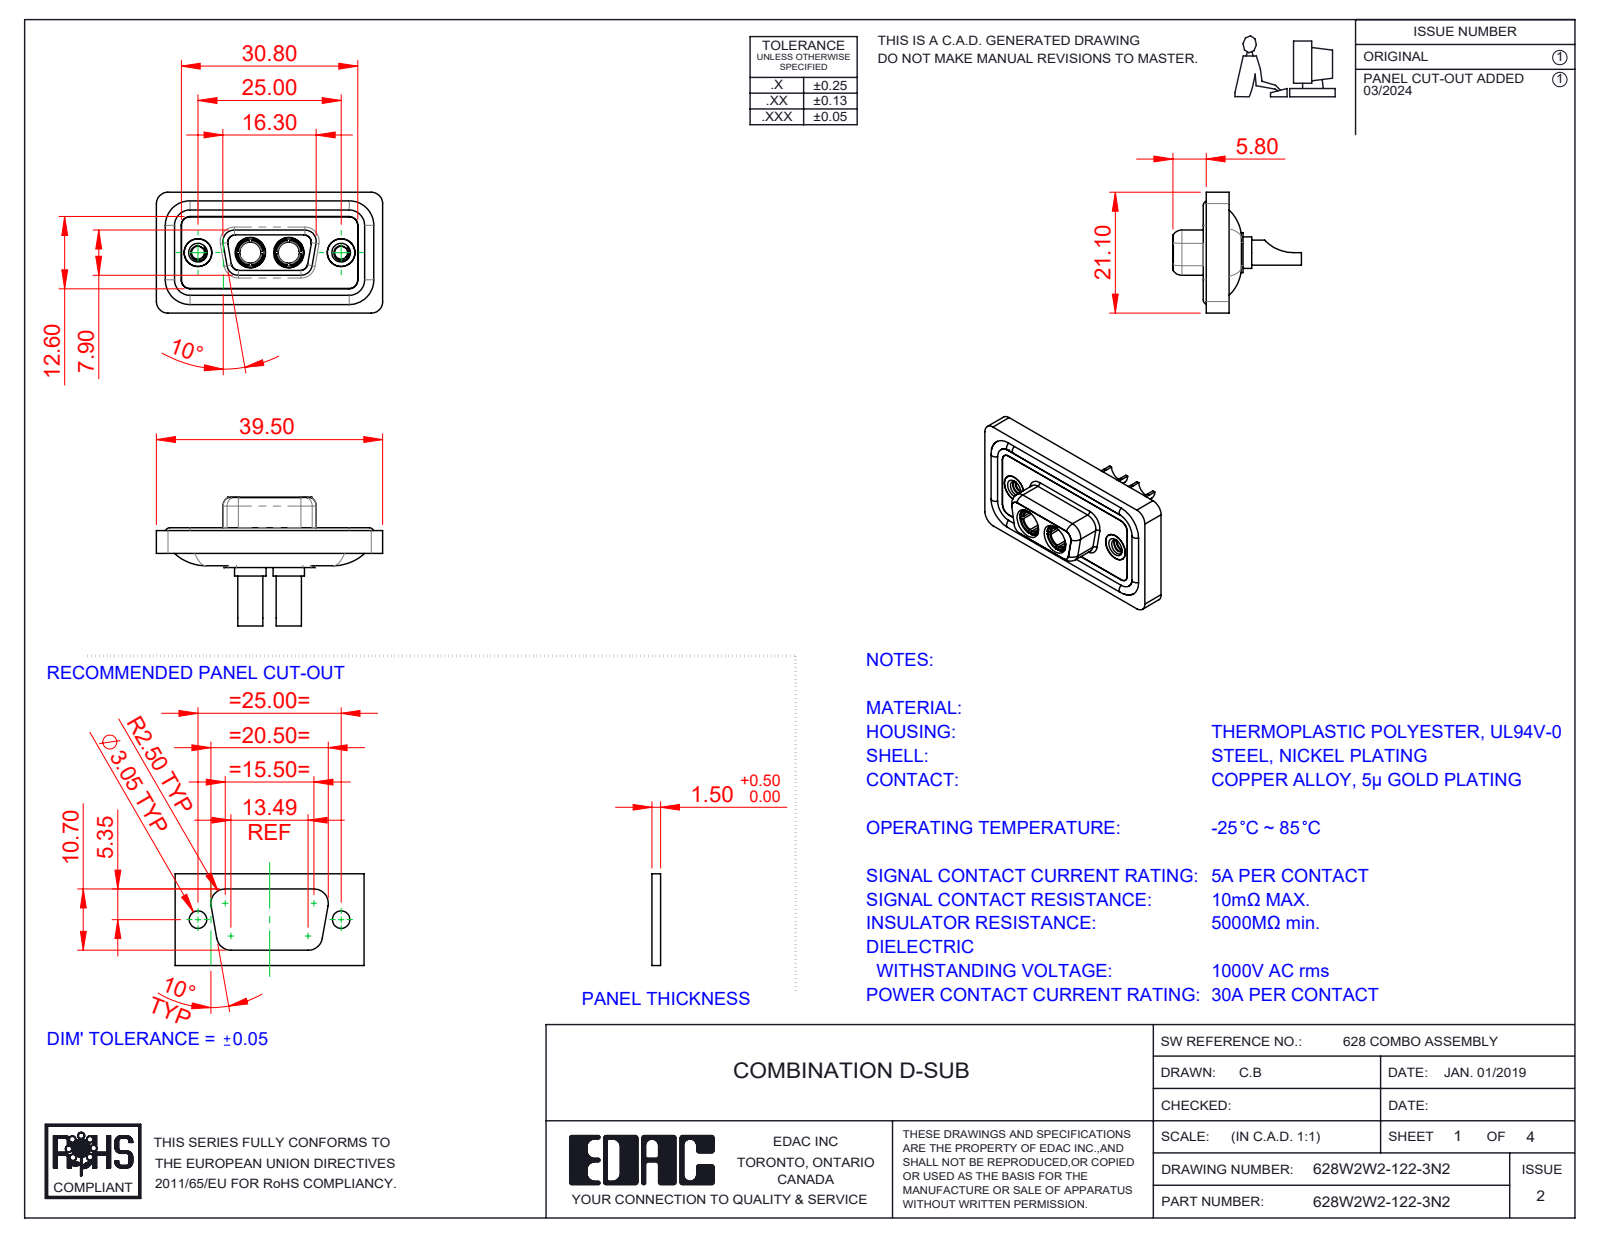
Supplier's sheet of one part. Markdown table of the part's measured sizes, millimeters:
| quantity | value |
| --- | --- |
| part name | 628Combo Shell Rear_09 Contacts; 628Combo Shell Front_09 Contacts; 628Combo Waterproof Housing_09 Contacts; 628W2W2-122-3N2 (+3 more) |
| STEP written by | SolidWorks 2023 (CONFIG_CONTROL_DESIGN) |
| units | millimeters |
| bodies | 11 solids, 546 faces (169 planar, 240 cylindrical, 137 other) |
| overall size | 39.5 × 22.45 × 21.1 |
| volume | 4 761 mm³ |
| surface area | 7 851 mm² |
| round holes (diameter × count) | 4.85 × 4, 2.26 × 2, 3.5 × 2, 3.7 × 2, 4 × 2, 4.05 × 2, 5 × 2, 5.3 × 2 |
| round bosses / shafts (diameter × count) | 1.6 × 4, 5.5 × 2, 5.2 × 2, 4.96 × 2, 4.95 × 2, 4.8 × 2, 4.75 × 2, 4.4 × 2 |
| partial cylindrical surfaces (radius × count) | 1.5 × 22, 2 × 18, 1.35 × 8, 1.6 × 8, 0.25 × 4, 0.5 × 4, 0.6 × 4, 0.65 × 4 |
| main face-to-face distances | 0.4, 1.1, 2.9, 1.8, 0.5, 1.6, 5.65, 7.45, 5.35, 3.1 |
| hole center spacings | 9.14, 15.86, 6.72, 25 |
